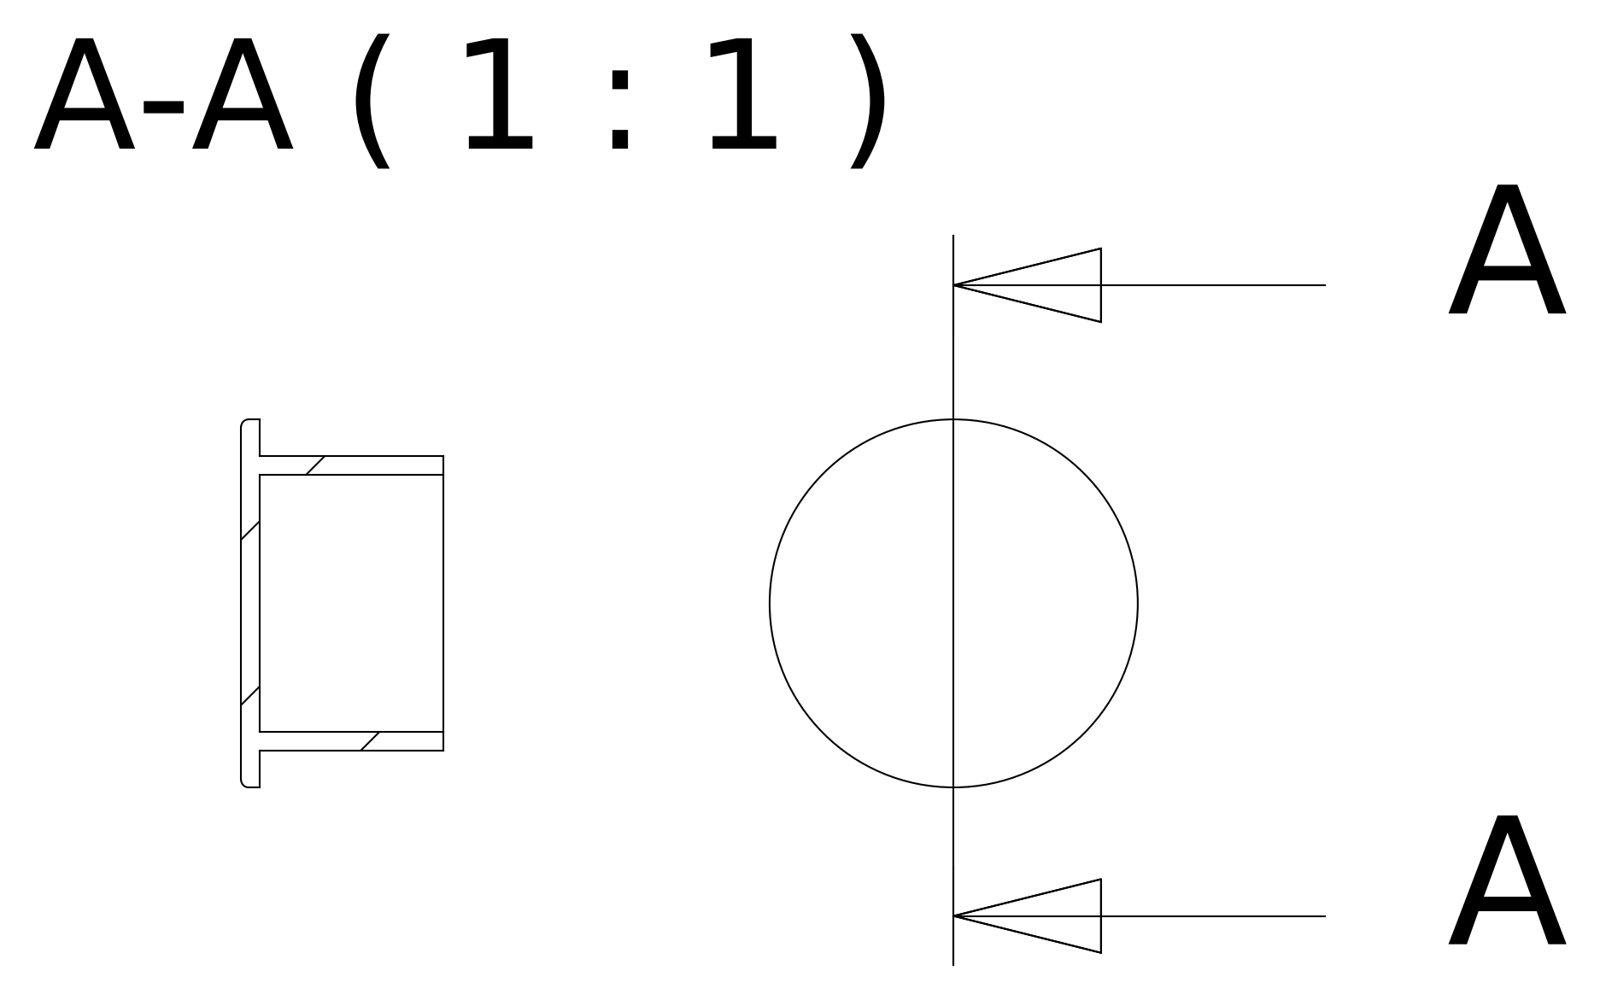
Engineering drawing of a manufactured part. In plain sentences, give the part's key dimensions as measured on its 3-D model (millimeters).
The part is named "18.065.00". Its 3-D file was written by "Autodesk Inventor 2016 (AUTOMOTIVE_DESIGN)". It is 1 solid with 8 faces: 4 planar, 3 cylindrical and 1 other. Overall it measures 10 by 10 by 5.5 millimeters. Its volume is 98 cubic millimeters and its surface area 406 square millimeters. Round holes: 1 of diameter 7. Round bosses or shafts: 1 of diameter 10, 1 of diameter 8. The main face-to-face distances are 0.5, 5, 5.5.
